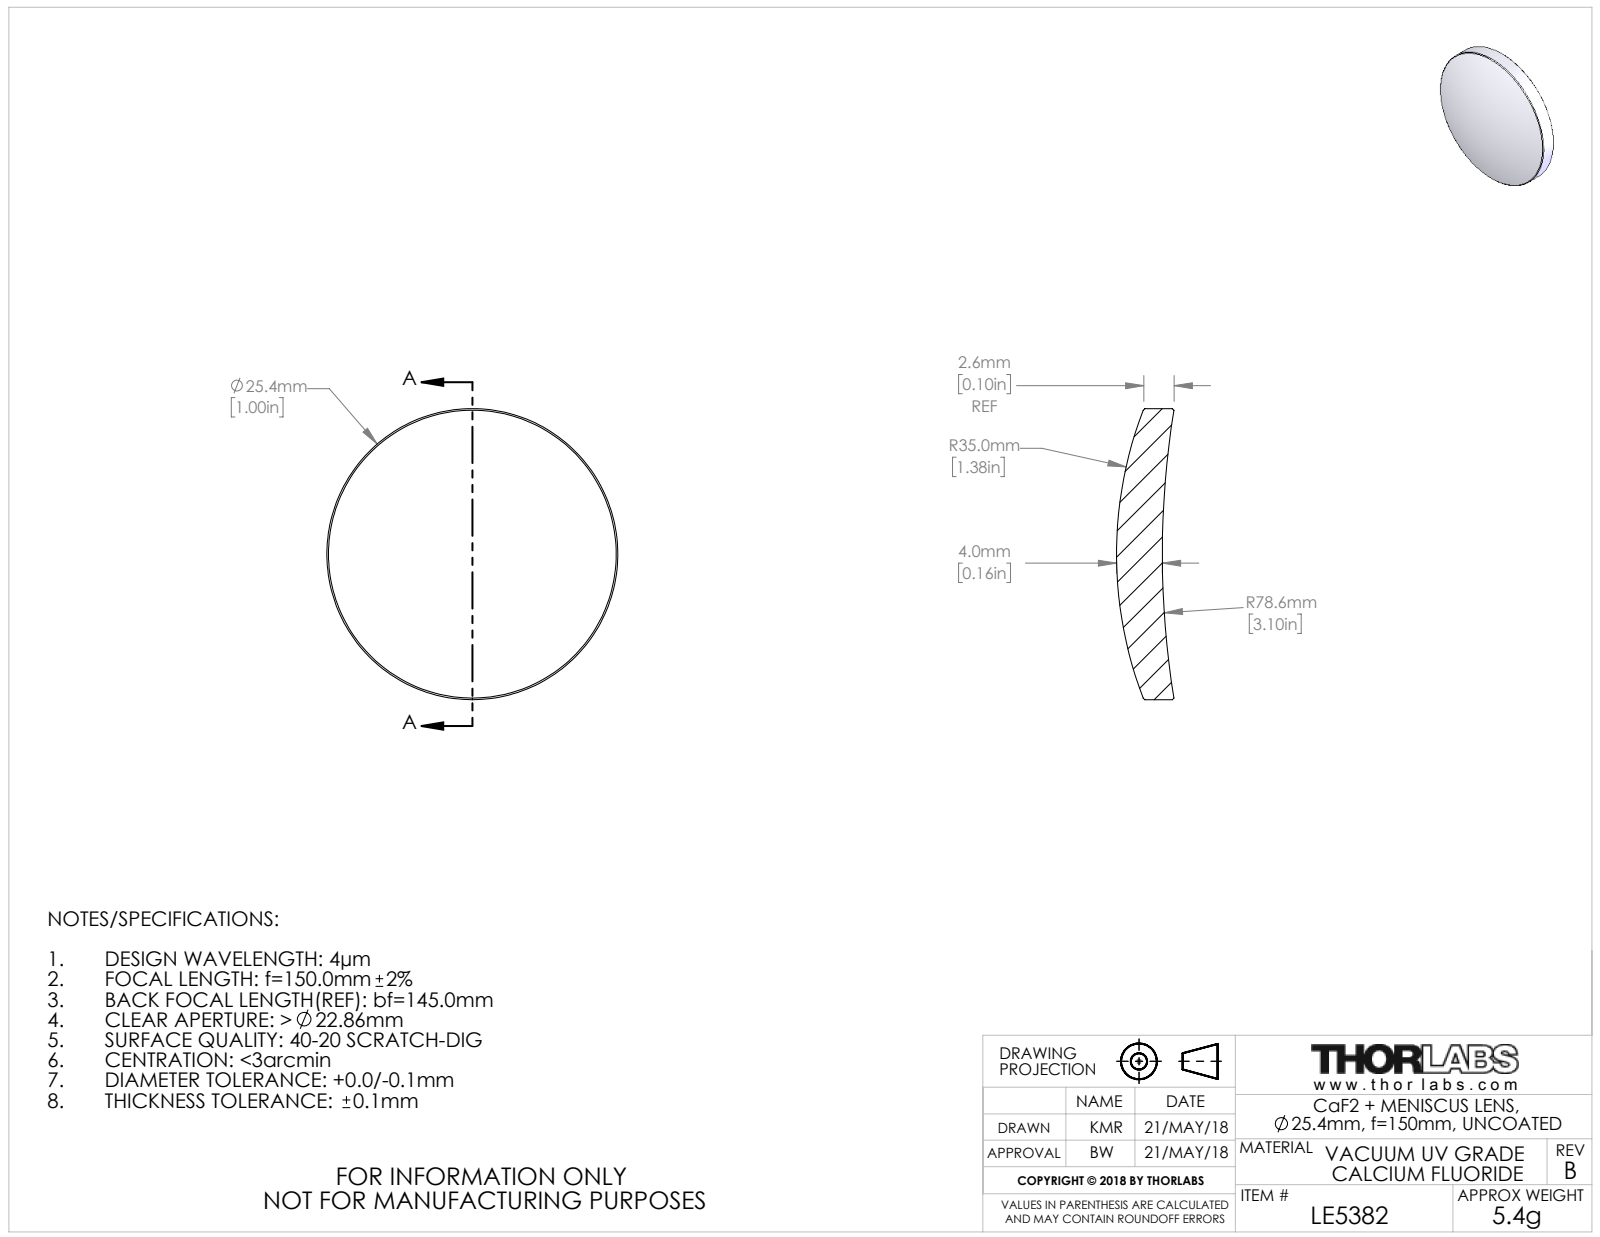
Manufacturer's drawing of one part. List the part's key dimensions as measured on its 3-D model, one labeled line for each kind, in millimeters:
Part name (STEP PRODUCT): 21990-E0W
STEP written by: SolidWorks 2016 (CONFIG_CONTROL_DESIGN)
Units: millimetres
Bodies: 1 solid, 10 faces (0 planar, 2 cylindrical, 8 other)
Overall size (bounding box): 25.4 × 25.4 × 5
Volume: 1 690 mm³ · Surface area: 1 234 mm²
Round bosses / shafts (diameter × count): ⌀25.4 ×1
